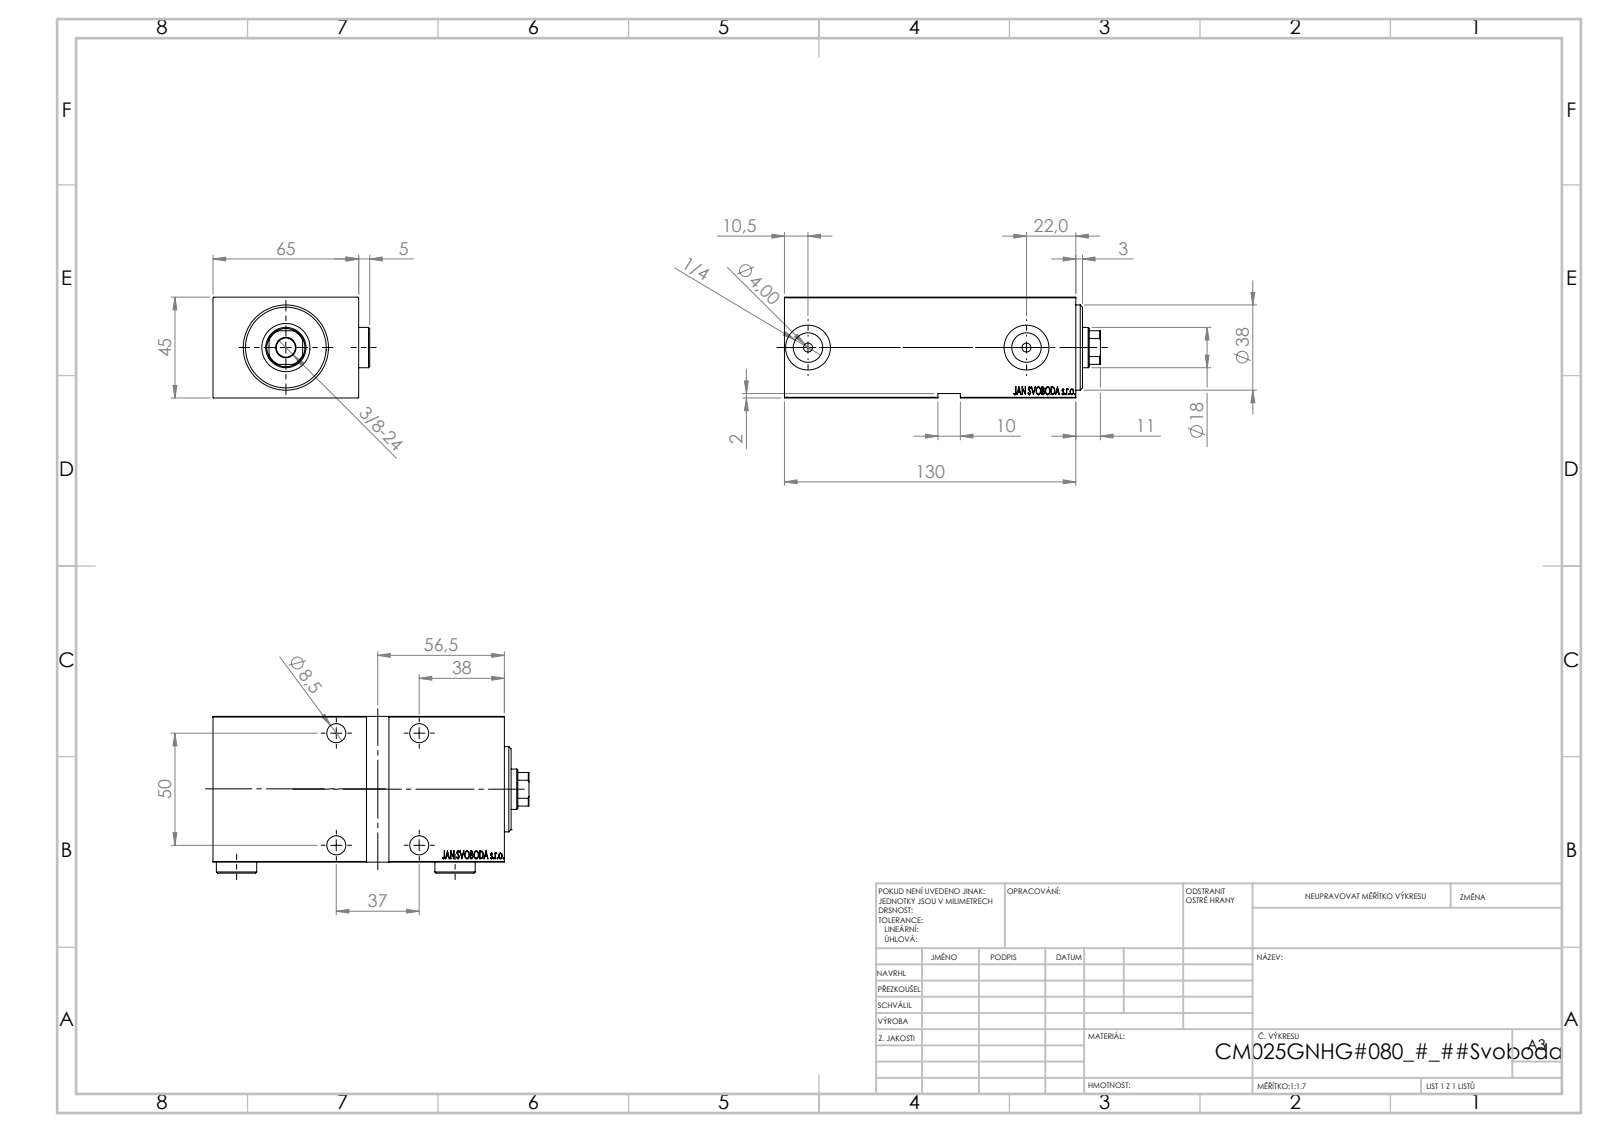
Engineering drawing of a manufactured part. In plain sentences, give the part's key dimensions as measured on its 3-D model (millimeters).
The part is named "V450CM_VC_G; Zatka_OIL_PORT; V450CM_G_Body; V450CM_G_VCP". Its 3-D file was written by "SolidWorks 2019 (CONFIG_CONTROL_DESIGN)". It is 5 solids with 897 faces: 441 planar, 58 cylindrical and 398 other. Overall it measures 141 by 69.9 by 45 millimeters. Its volume is 348 278 cubic millimeters and its surface area 66 193 square millimeters. Round holes: 5 of diameter 8.5, 4 of diameter 13.5, 2 of diameter 4, 2 of diameter 13.16, 2 of diameter 20, 1 of diameter 18, 1 of diameter 21.5, 1 of diameter 25, 1 of diameter 27, 1 of diameter 35. Round bosses or shafts: 2 of diameter 18, 1 of diameter 38. Partial cylindrical surfaces (rounded edges, fillets, slot ends): 1 of radius 8.5. The main face-to-face distances are 45, 65, 130, 6, 119, 5, 124, 64.9, 8, 125. The hole center spacings are 37, 50, 62.2, 97.5.
